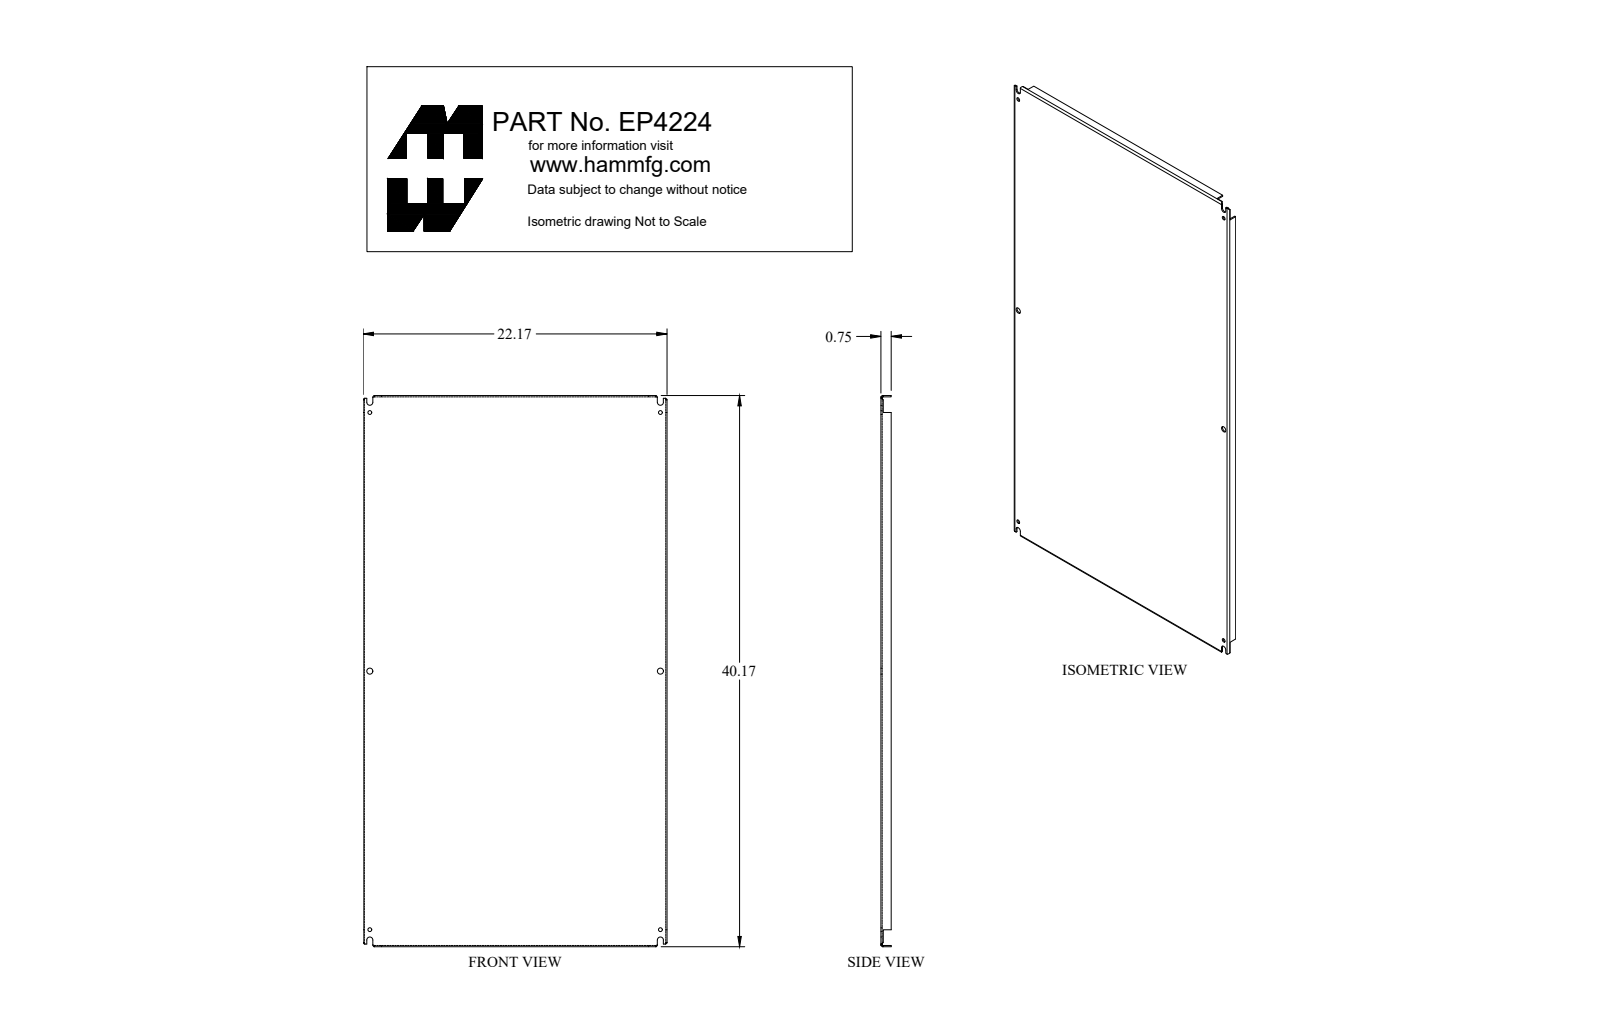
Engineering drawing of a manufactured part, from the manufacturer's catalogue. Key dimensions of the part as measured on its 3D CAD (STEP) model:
Part name (STEP PRODUCT): EP4224
STEP written by: SolidWorks 2018 (AUTOMOTIVE_DESIGN)
Units: inches
Bodies: 1 solid, 88 faces (50 planar, 30 cylindrical, 8 other)
Overall size (bounding box): 40.17 × 22.17 × 0.75
Volume: 88.82 in³ · Surface area: 1 883 in²
Round holes (diameter × count): ⌀0.281 ×4, ⌀0.437 ×2
Partial cylindrical surfaces — rounded edges, fillets, slot ends (radius × count): R0.219 ×4, R0.048 ×2, R0.063 ×2, R0.143 ×2
Main face-to-face distances: 0.095, 22.075, 22.17, 21.98, 0.75, 0.655, 40.17, 0.171, 0.076, 0.579
Hole centre spacings: 18.844, 28.356, 21.188, 37.688, 43.236
